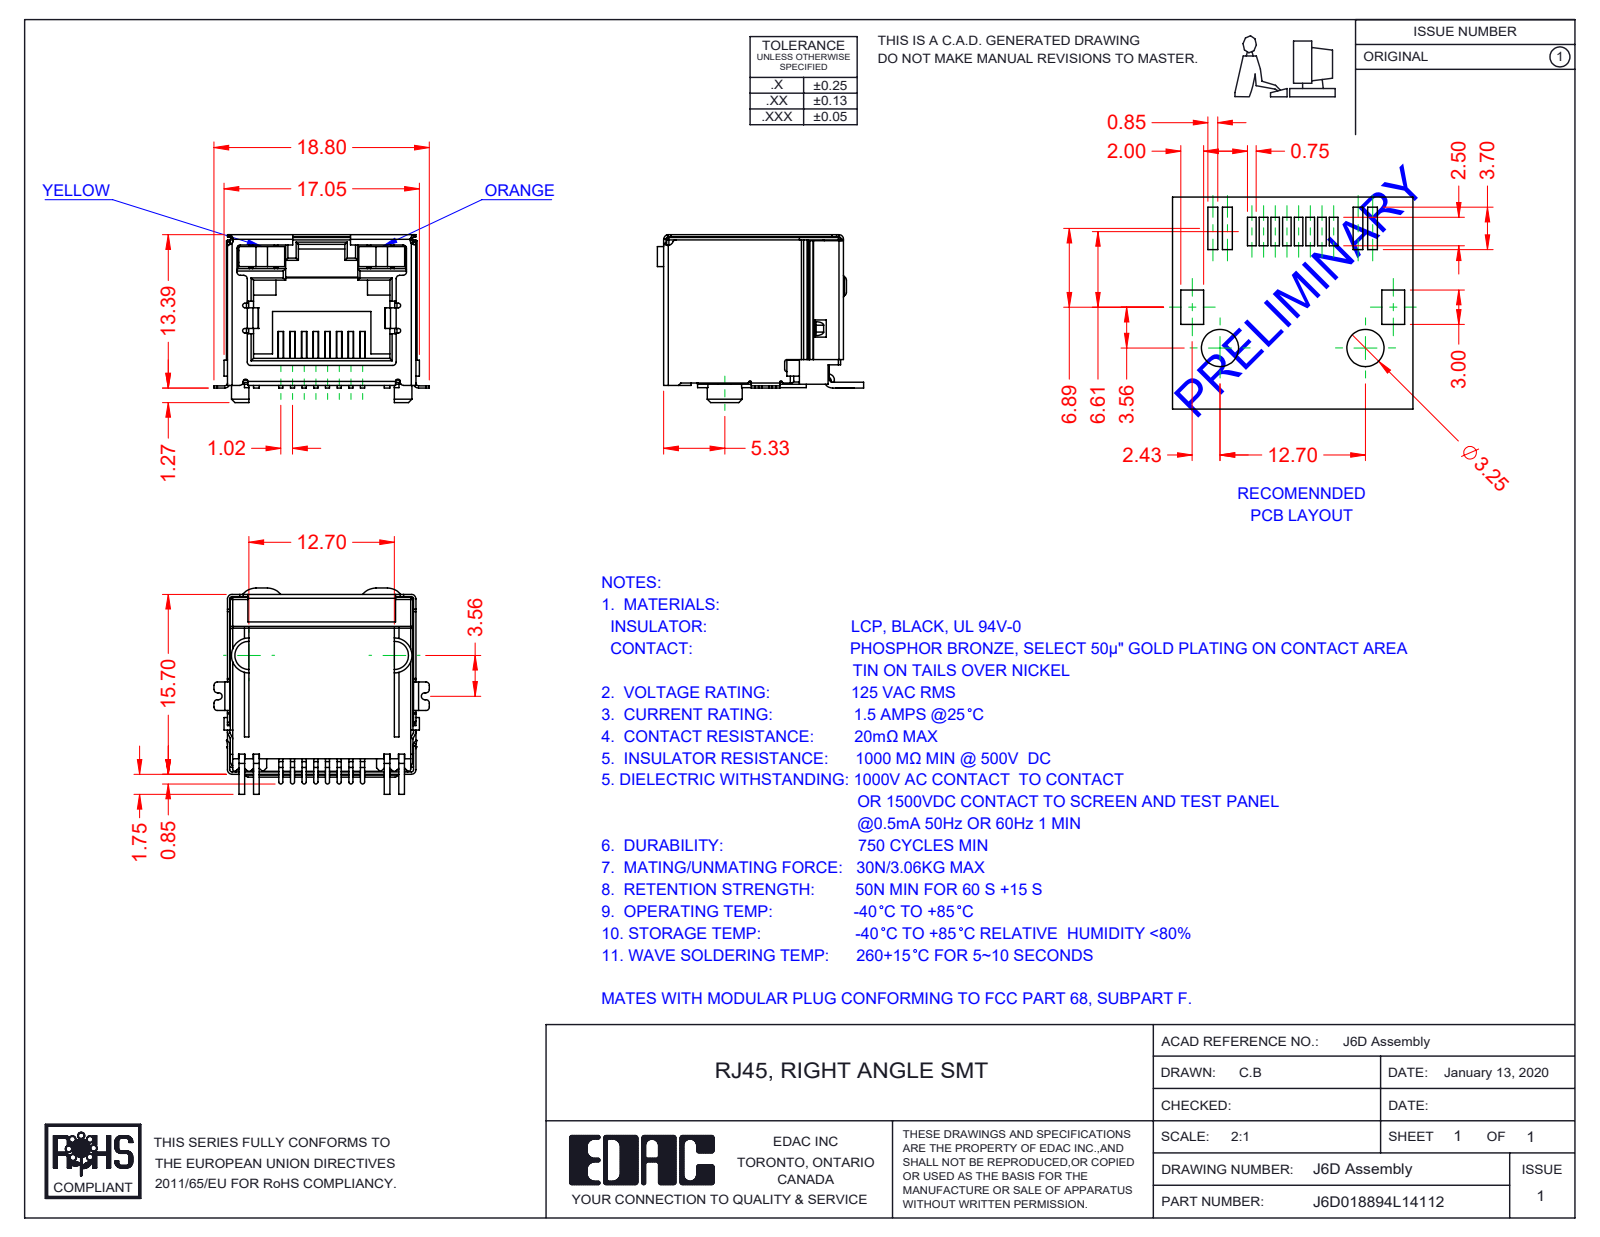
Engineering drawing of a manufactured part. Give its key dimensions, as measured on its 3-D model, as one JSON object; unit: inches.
{"part_name": "6D Insulator; 6D Shield_LED - No EMI; 6D LED LH_1-Yellow; 6D Contacts (+2 more)", "step_written_by": "SolidWorks 2016 (CONFIG_CONTROL_DESIGN)", "units": "inches", "bodies": {"solids": 12, "faces": 893, "planar": 644, "cylindrical": 216, "other": 33}, "overall_size": [0.74, 0.709, 0.577], "volume_in3": 0.11, "surface_area_in2": 7.592, "partial_cylinders_radius": [[0.012, 39], [0.008, 37], [0.016, 16], [0.004, 12], [0.006, 8], [0.007, 8], [0.02, 6], [0.059, 5]], "face_to_face_distances": [0.63, 0.64, 0.638, 0.089, 0.039, 0.628, 0.632, 0.504, 0.018, 0.648]}
